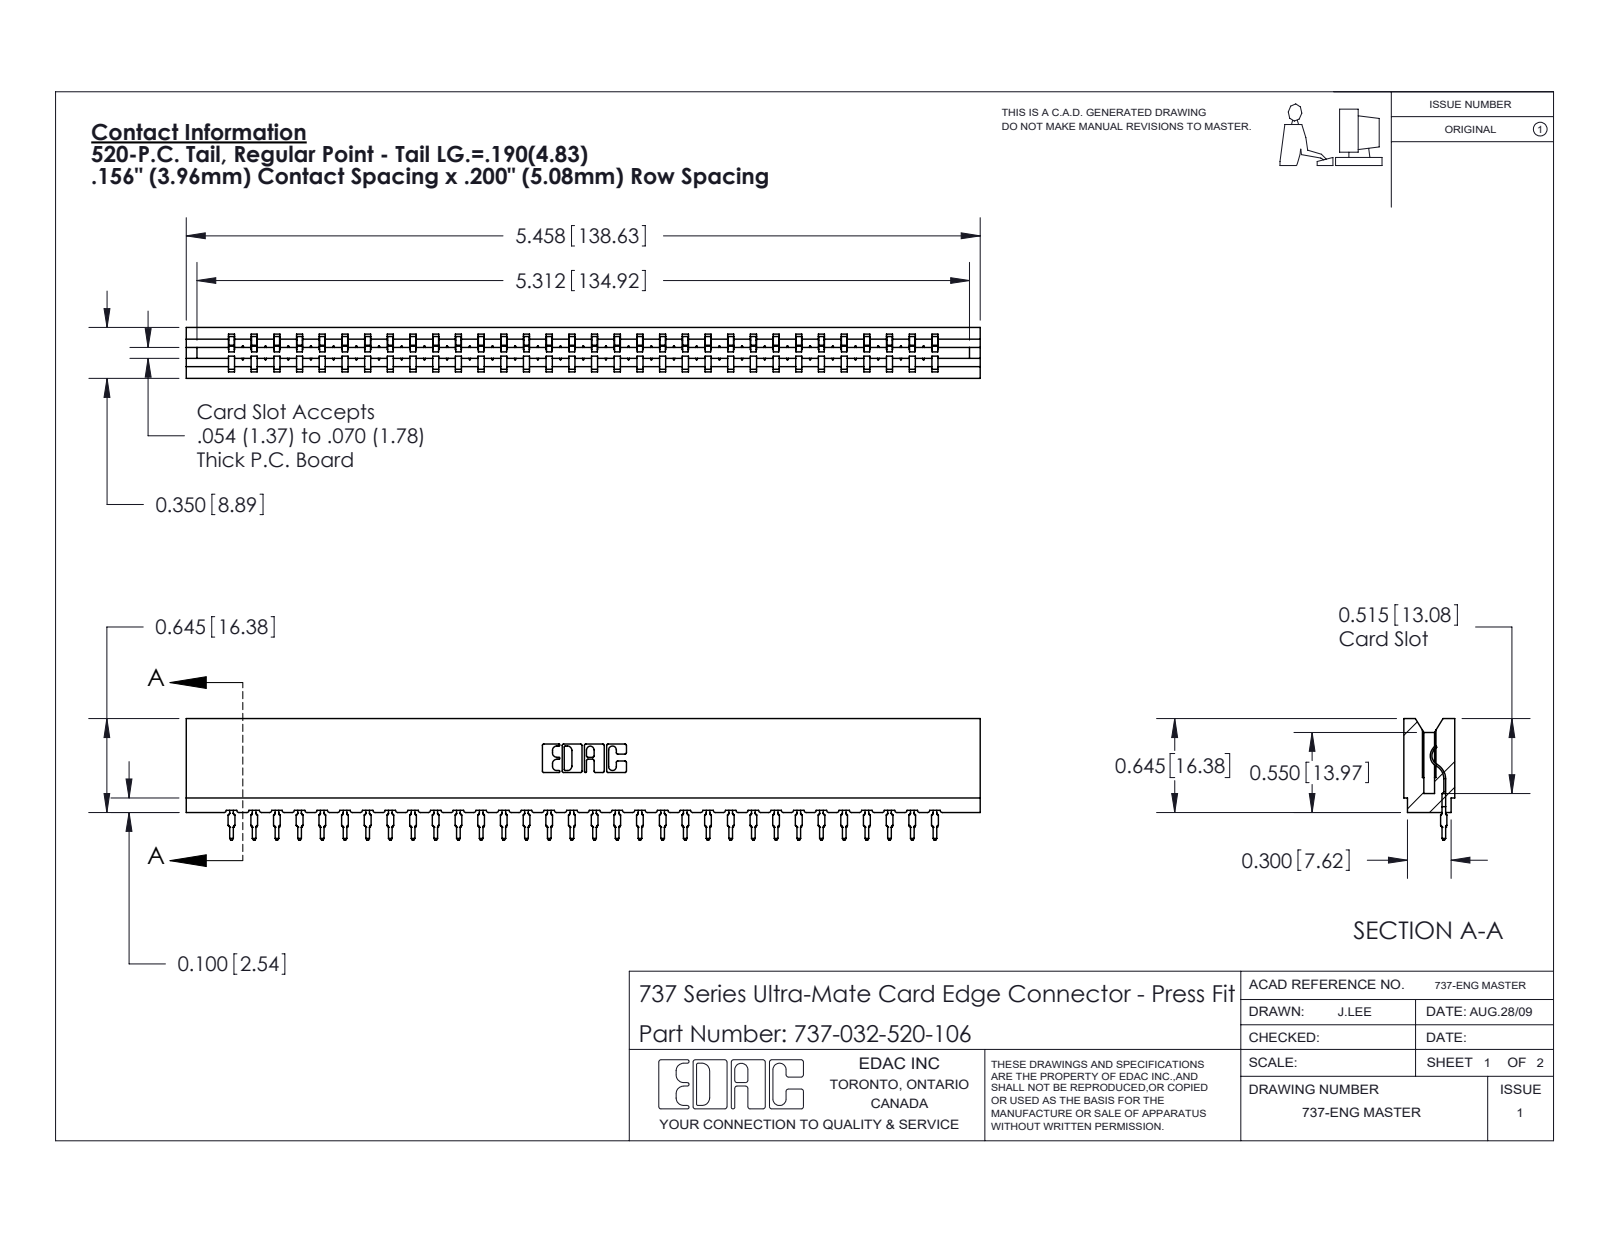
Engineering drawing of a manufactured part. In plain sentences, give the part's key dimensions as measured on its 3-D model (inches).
The part is named "737 Part_Insulator Option - 06; 737-032-520-106; 745-292-001_520". Its 3-D file was written by "SolidWorks 2020 (CONFIG_CONTROL_DESIGN)". It is 33 solids with 3711 faces: 2231 planar, 648 cylindrical and 832 other. Overall it measures 5.458 by 0.836 by 0.35 inches. Its volume is 0.818 cubic inches and its surface area 27.31 square inches. Partial cylindrical surfaces (rounded edges, fillets, slot ends): 64 of radius 0.015, 64 of radius 0.021, 22 of radius 0.01, 6 of radius 0.007, 6 of radius 0.031, 4 of radius 0.005, 4 of radius 0.011, 3 of radius 0.026. The main face-to-face distances are 0.138, 0.212, 0.35, 0.074, 0.045, 0.305, 0.093, 0.167, 0.624, 0.156.
